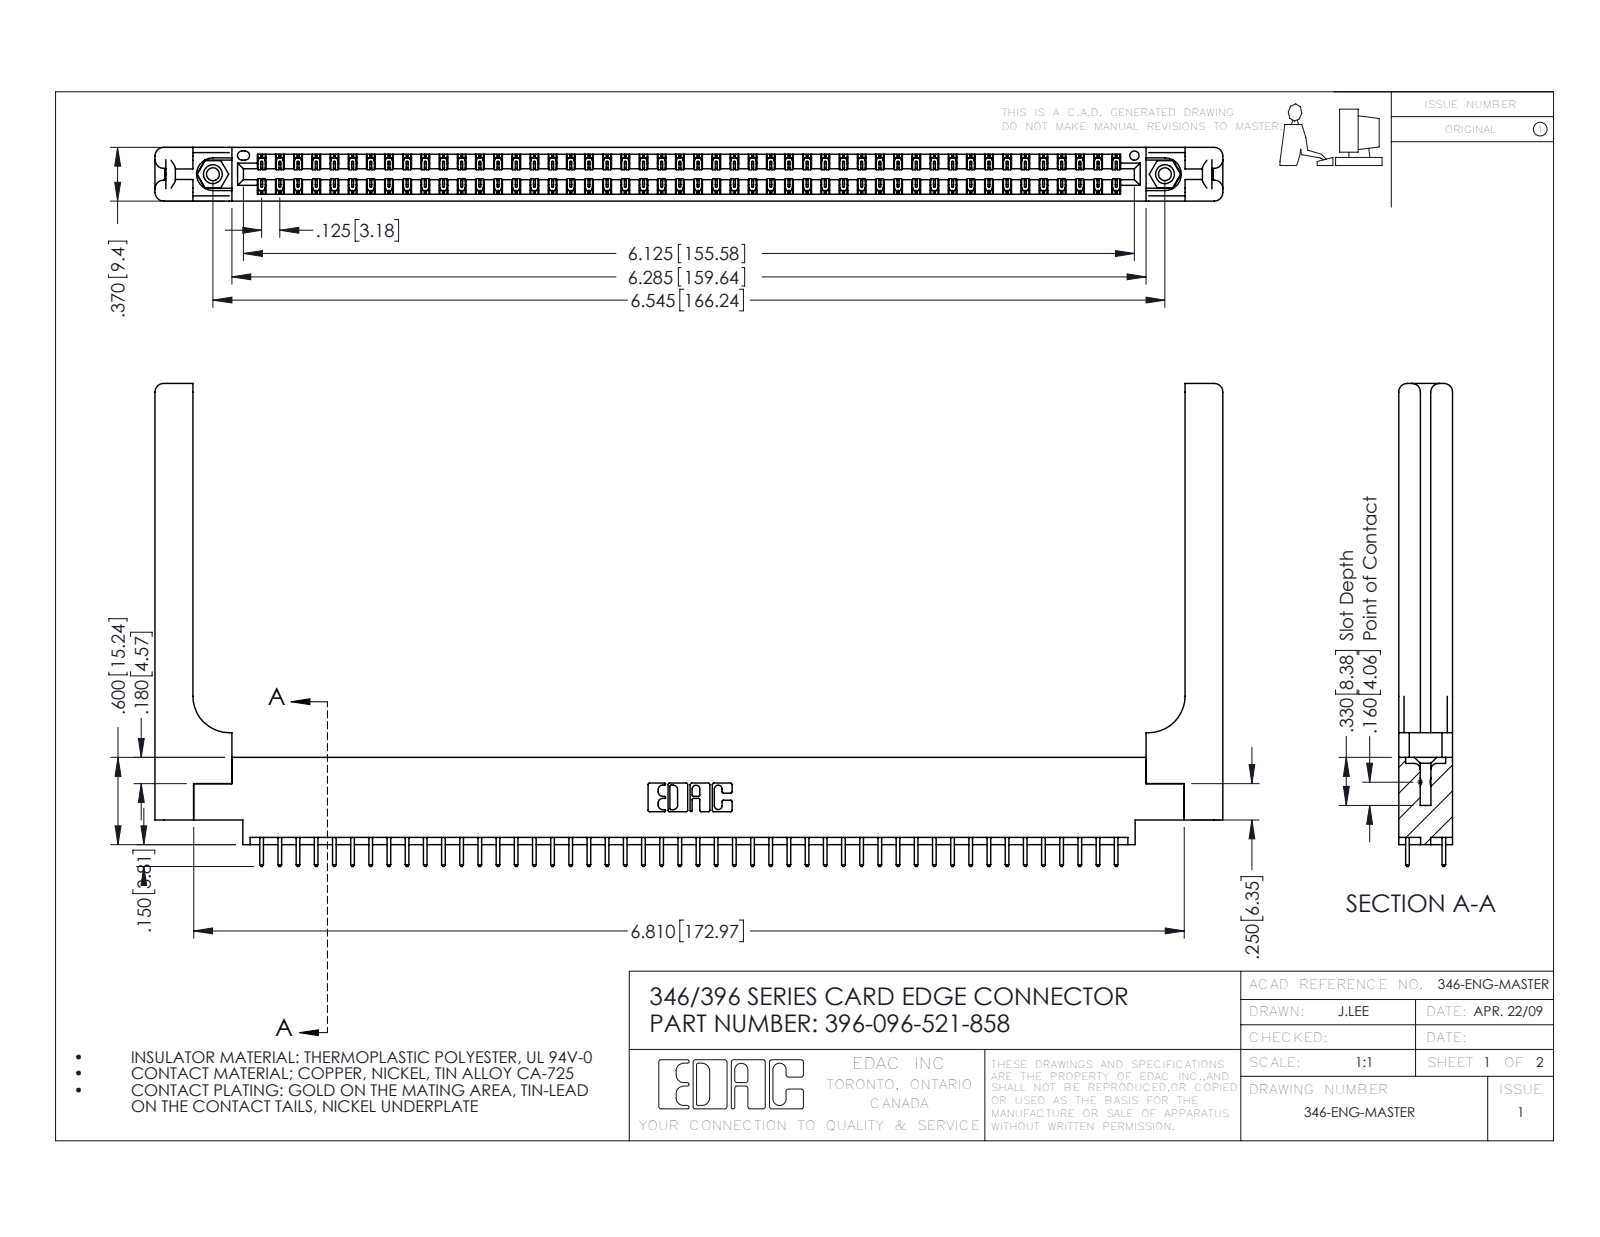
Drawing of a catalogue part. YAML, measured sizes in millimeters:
part_name: "396-096-521-858; 346-220-058_345-220-058; 345-250-001_345-250-001-102; 345-292-001_345-293-121 (+1 more)"
step_written_by: "SolidWorks 2016 (CONFIG_CONTROL_DESIGN)"
units: millimeters
bodies: {solids: 101, faces: 5374, planar: 3588, cylindrical: 1726, other: 60}
overall_size: [186.5, 84.3, 9.4]
volume: 25530
surface_area: 29770
round_holes:
  - {diameter: 2.3, count: 2}
  - {diameter: 3.2, count: 2}
  - {diameter: 4, count: 2}
  - {diameter: 1.6, count: 1}
round_bosses_or_shafts:
  - {diameter: 3.9, count: 2}
partial_cylinders:
  - {radius: 0.2, count: 144}
  - {radius: 0.3, count: 96}
  - {radius: 0.3, count: 22}
  - {radius: 1.5, count: 16}
  - {radius: 0.2, count: 6}
  - {radius: 0.8, count: 6}
  - {radius: 0.7, count: 3}
  - {radius: 0.4, count: 2}
face_to_face_distances: [9.4, 1.2, 8.2, 1.8, 6.4, 3.8, 3.8, 0.6, 7.6, 7]
hole_center_spacings: [6.2, 160.9, 166.2]
